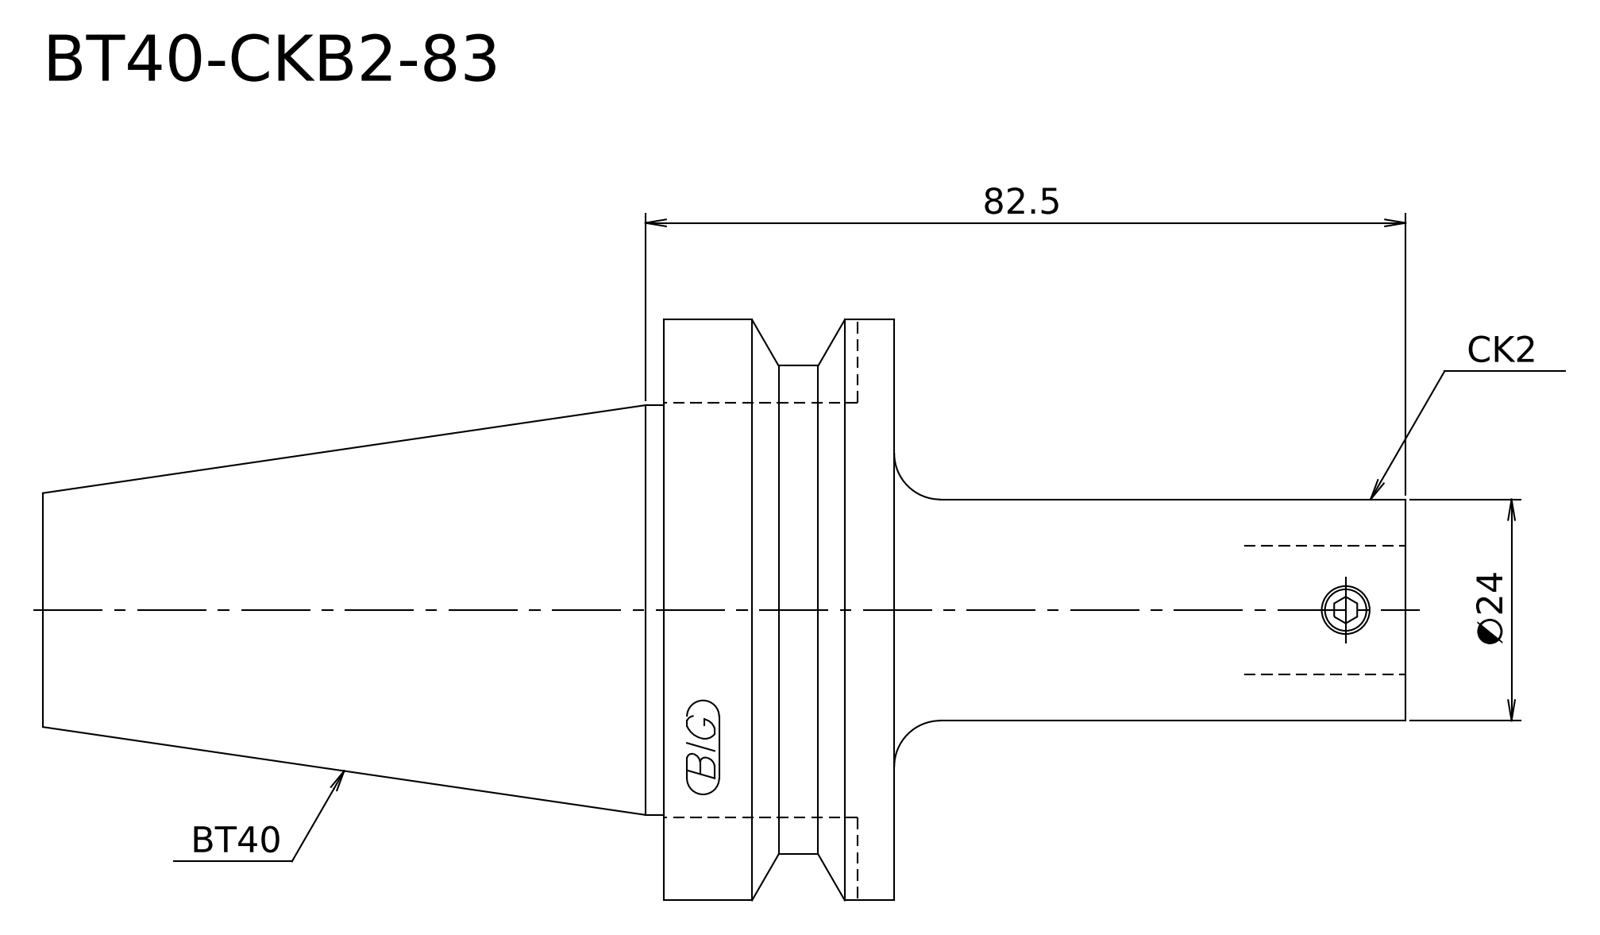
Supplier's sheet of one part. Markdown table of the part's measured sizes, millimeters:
| quantity | value |
| --- | --- |
| STEP written by | Kubotek KeyCreator V8.5.1 (14335) (CONFIG_CONTROL_DESIGN) |
| units | millimeters |
| bodies | 1 solid, 14 faces (4 planar, 5 cylindrical, 5 other) |
| overall size | 147.9 × 63 × 63 |
| volume | 164 804 mm³ |
| surface area | 22 456 mm² |
| round bosses / shafts (diameter × count) | 63 × 1, 53 × 1, 44.45 × 1, 24 × 1 |
| main face-to-face distances | 25, 92.4, 67.4, 55.5, 80.5, 147.9 |
